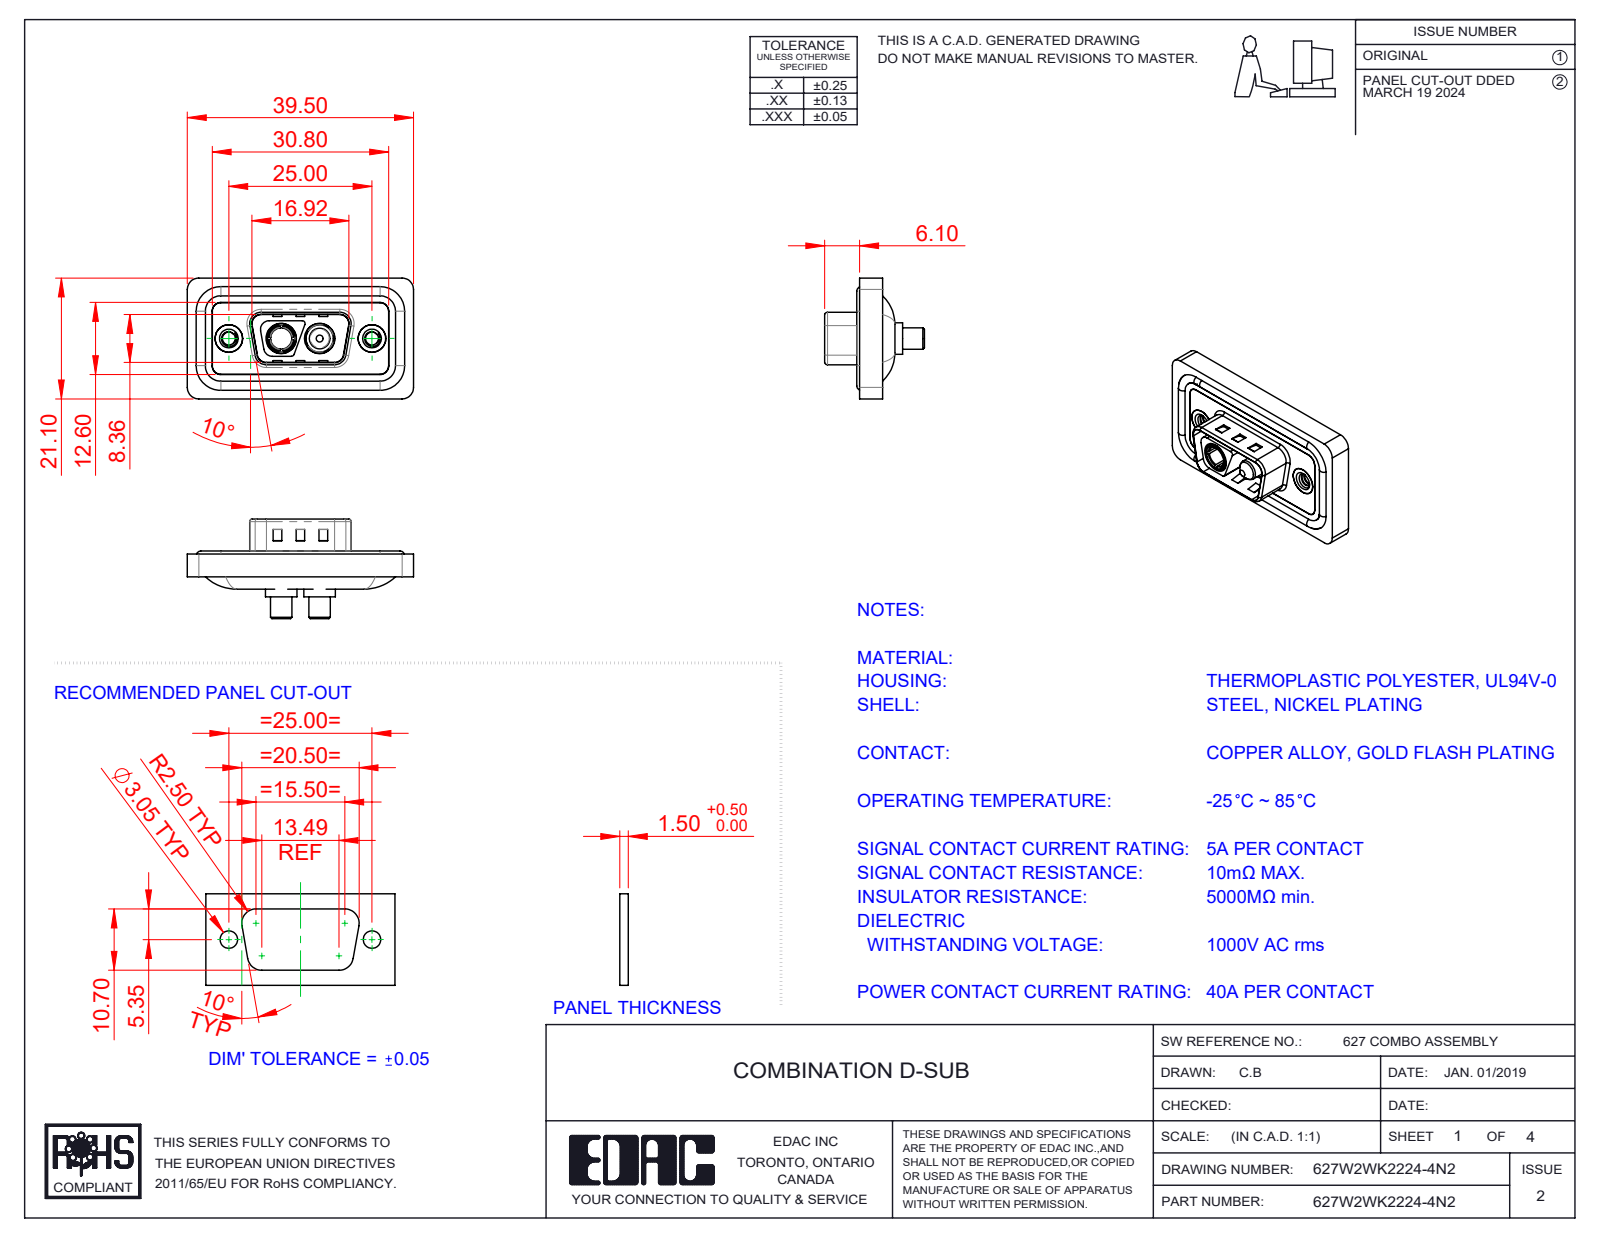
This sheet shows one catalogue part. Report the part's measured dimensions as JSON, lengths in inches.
{"part_name": "627Combo Threaded Rivet_2; 627Combo Housing_2WK2; 627W2WK2224-4N2; 627Combo Shell Rear_09 Contacts (+4 more)", "step_written_by": "SolidWorks 2023 (CONFIG_CONTROL_DESIGN)", "units": "inches", "bodies": {"solids": 11, "faces": 534, "planar": 189, "cylindrical": 227, "other": 118}, "overall_size": [1.555, 0.831, 0.685], "volume_in3": 0.28, "surface_area_in2": 11.41, "round_holes": [[0.089, 2], [0.157, 2], [0.189, 2], [0.191, 2], [0.197, 2], [0.209, 2], [0.146, 1]], "round_bosses_or_shafts": [[0.063, 4], [0.217, 2], [0.205, 2], [0.193, 2], [0.187, 2], [0.148, 2], [0.195, 1], [0.142, 1]], "partial_cylinders_radius": [[0.059, 24], [0.079, 18], [0.02, 10], [0.063, 8], [0.01, 4], [0.024, 4], [0.026, 4], [0.035, 4]], "face_to_face_distances": [0.016, 0.043, 0.114, 0.02, 0.122, 0.063, 0.059, 0.098, 0.157, 0.071], "hole_center_spacings": [0.36, 0.624, 0.265, 0.984]}
